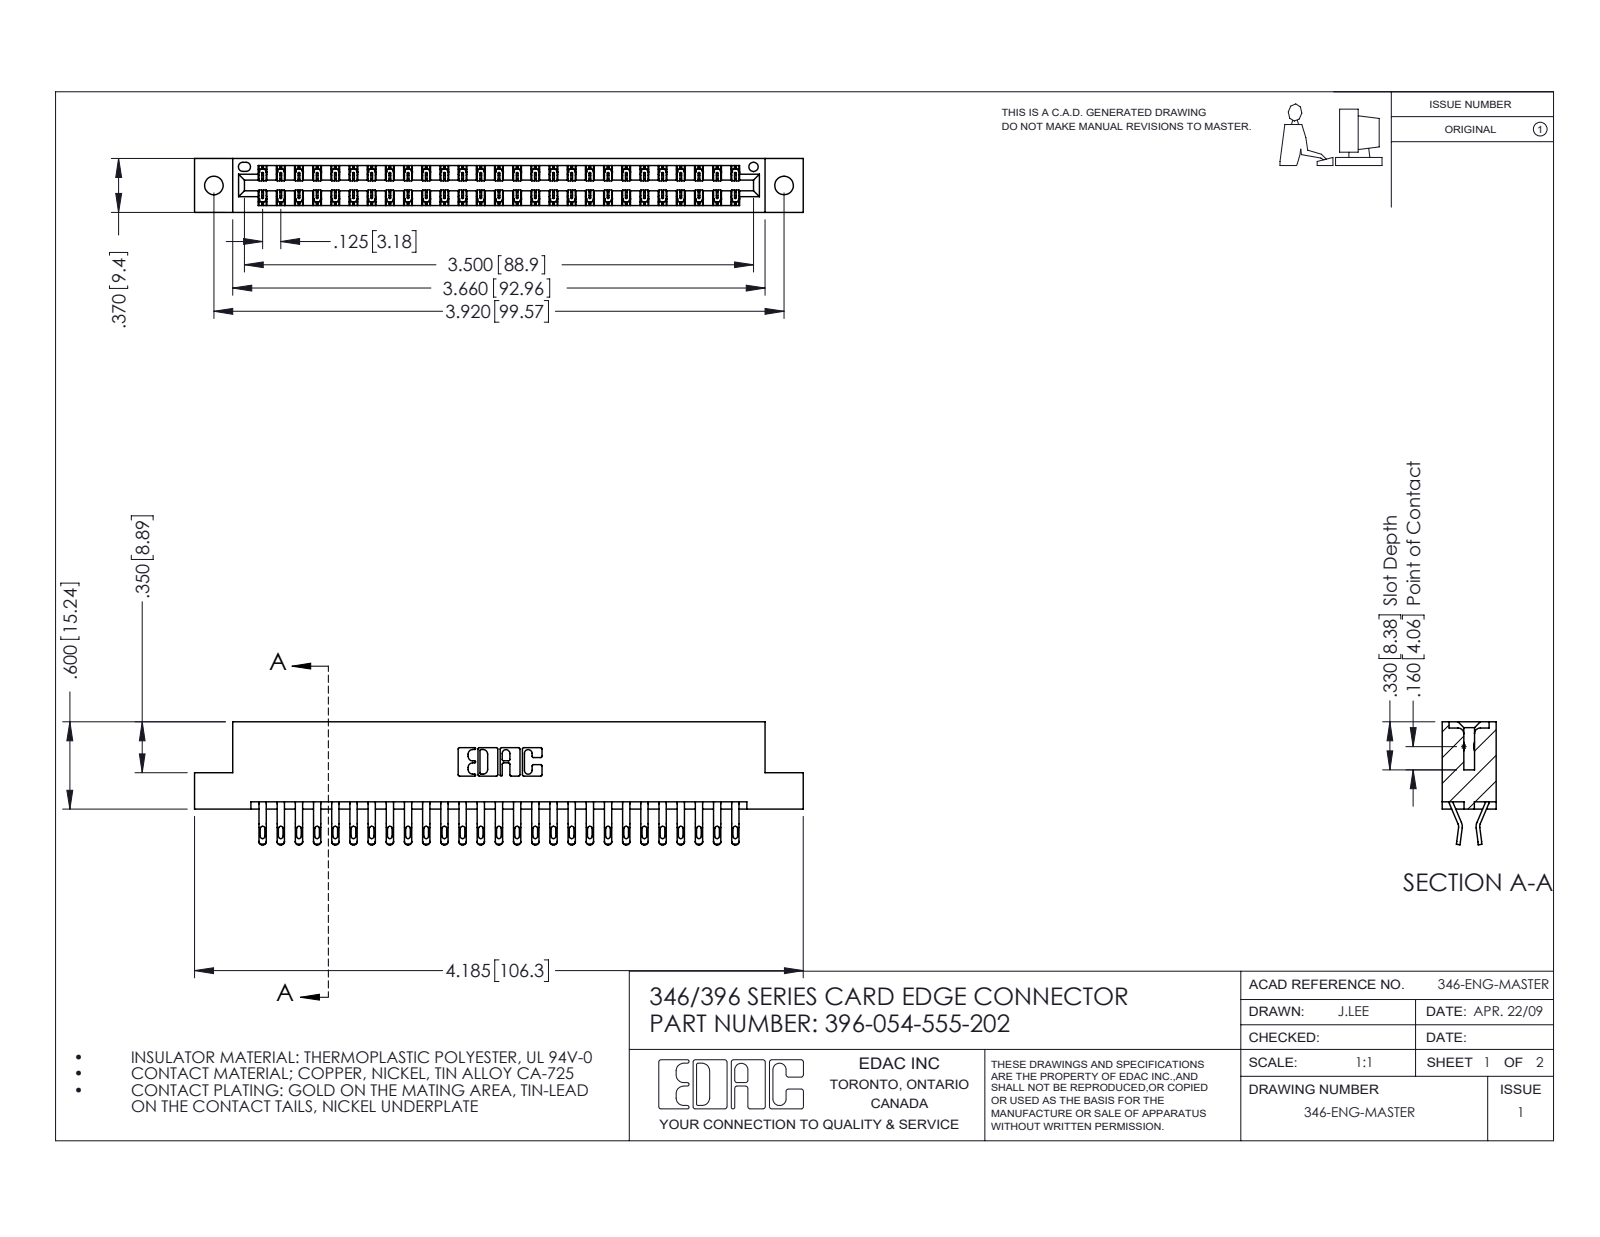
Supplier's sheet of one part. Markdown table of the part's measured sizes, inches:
| quantity | value |
| --- | --- |
| part name | 346 Part_Flush Mounting Lugs - 0.128 Dia; 345-292-001_555 Tail; 396-054-555-202 |
| STEP written by | SolidWorks 2016 (CONFIG_CONTROL_DESIGN) |
| units | inches |
| bodies | 55 solids, 3254 faces (1858 planar, 1396 cylindrical, 0 other) |
| overall size | 4.185 × 0.845 × 0.37 |
| volume | 0.633 in³ |
| surface area | 22.17 in² |
| round holes (diameter × count) | 0.128 × 2, 0.064 × 1 |
| partial cylindrical surfaces (radius × count) | 0.016 × 108, 0.02 × 108, 0.006 × 81, 0.01 × 22, 0.007 × 6, 0.031 × 6, 0.026 × 3, 0.01 × 2 |
| main face-to-face distances | 0.048, 0.322, 0.37, 0.25, 0.025, 0.072, 0.298, 0.275, 0.148, 0.222 |
| hole center spacings | 0.246, 3.712, 3.92 |
